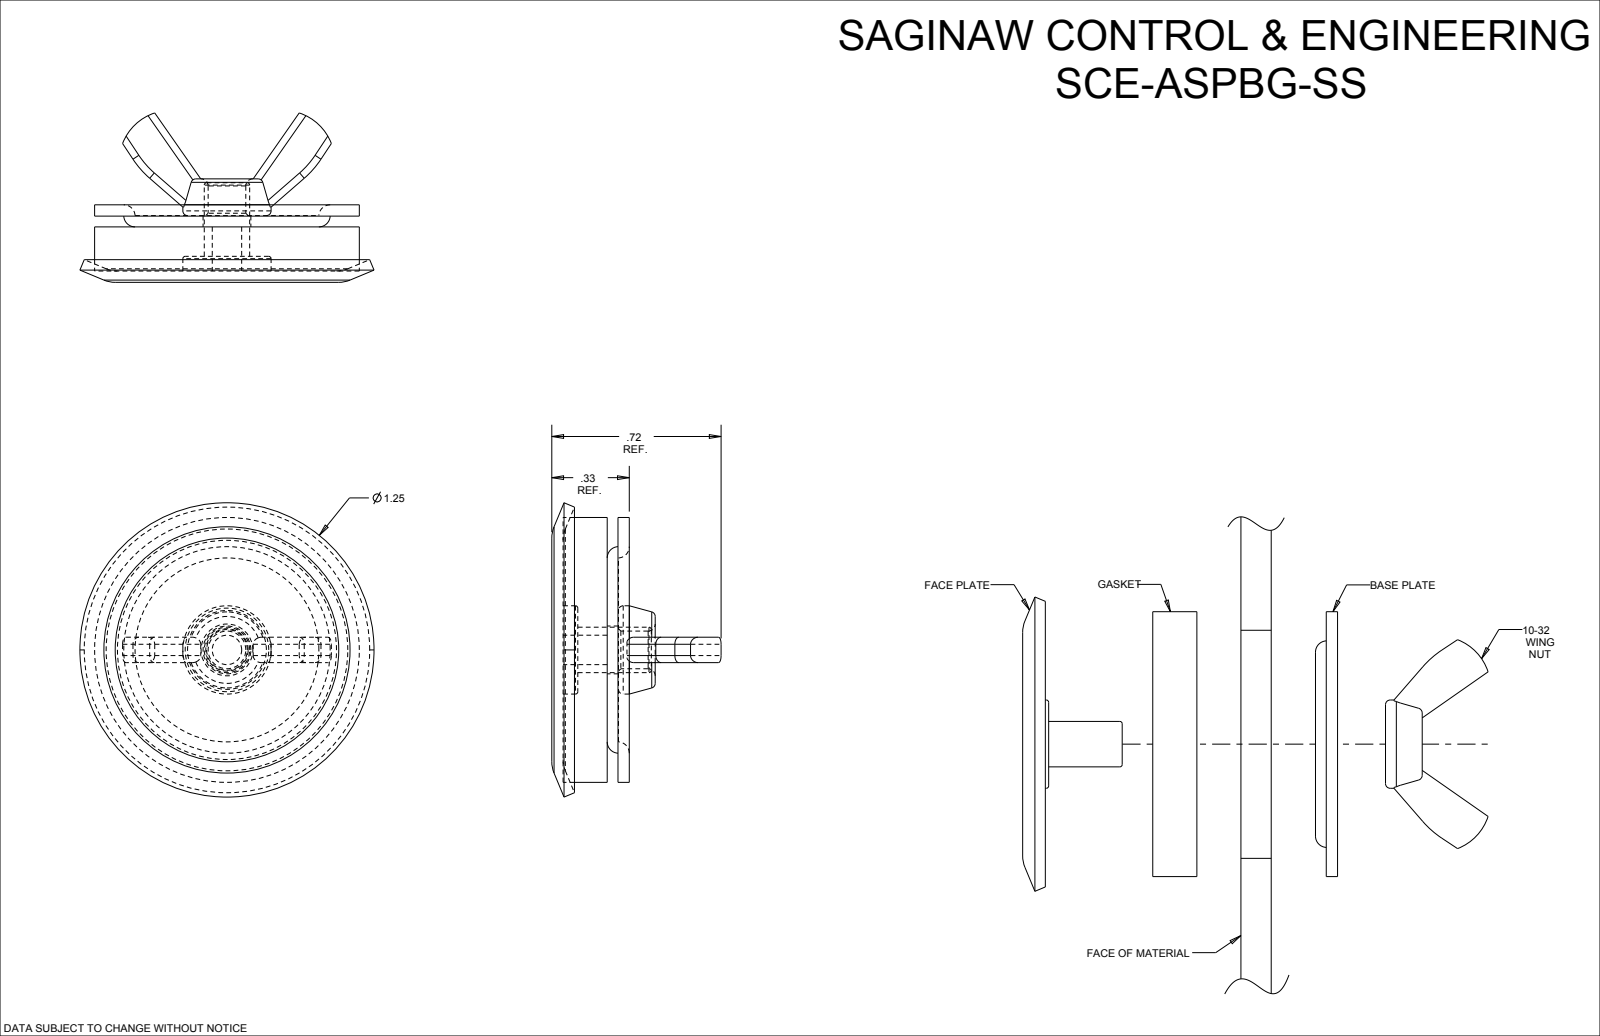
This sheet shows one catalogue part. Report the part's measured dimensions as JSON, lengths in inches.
{"part_name": "SCE-ASPBG-SS", "step_written_by": "SolidWorks 2019 (CONFIG_CONTROL_DESIGN)", "units": "inches", "bodies": {"solids": 5, "faces": 71, "planar": 27, "cylindrical": 24, "other": 20}, "overall_size": [1.25, 1.25, 0.719], "volume_in3": 0.333, "surface_area_in2": 8.822, "round_holes": [[0.125, 1], [0.16, 1], [0.203, 1]], "round_bosses_or_shafts": [[1.125, 1], [0.375, 1], [0.193, 1]], "partial_cylinders_radius": [[0.03, 12], [0.22, 2], [0.4, 2]], "face_to_face_distances": [0.048, 0.187, 0.235, 0.046, 0.281, 0.283, 0.094, 0.329, 0.233, 0.108]}
